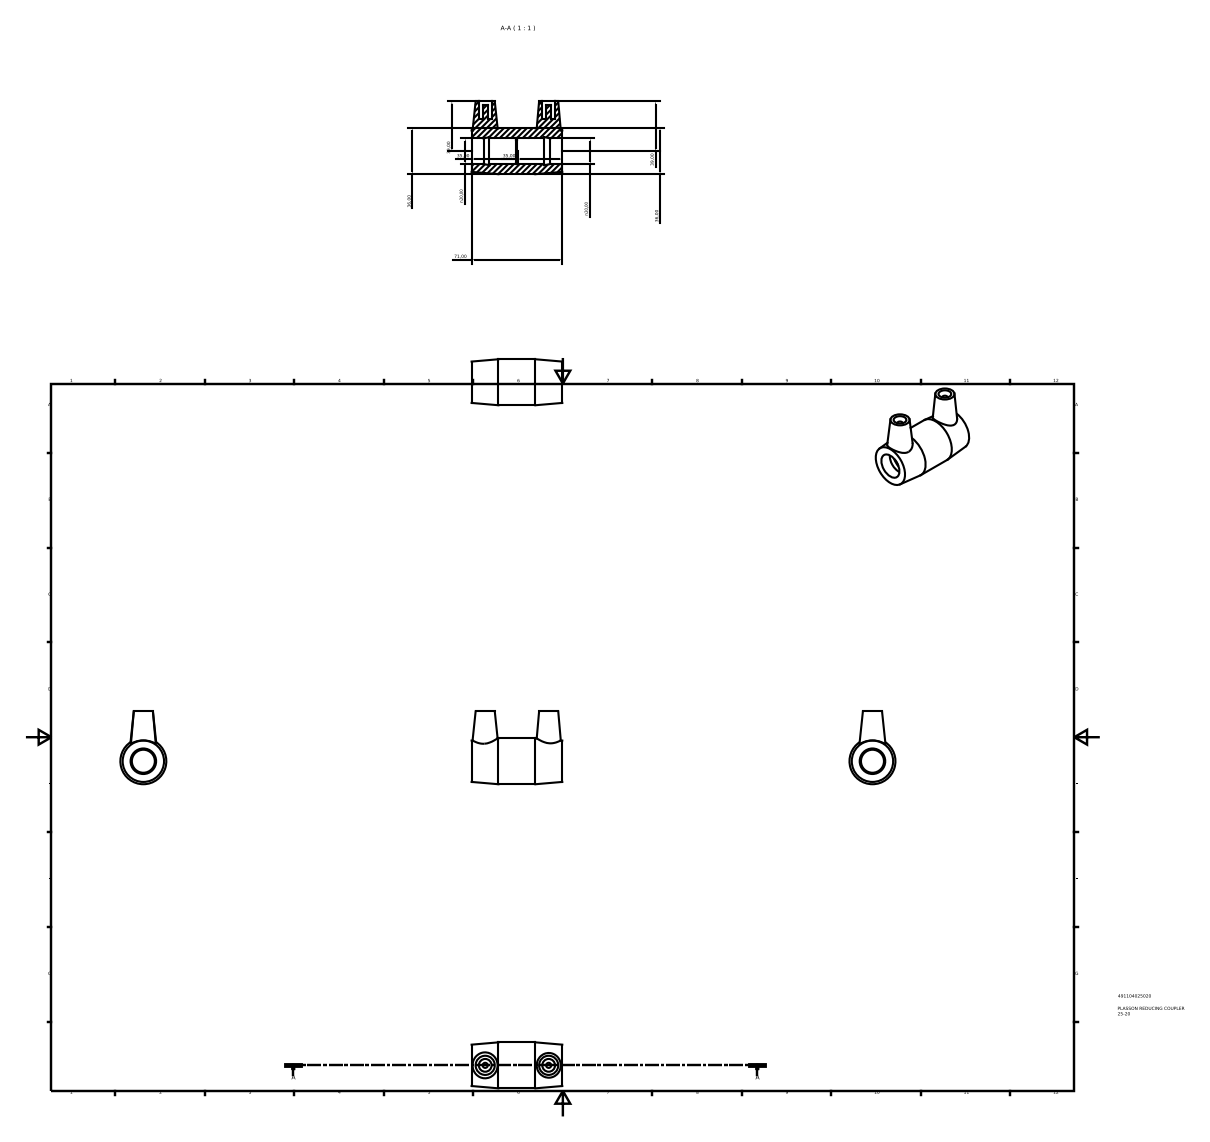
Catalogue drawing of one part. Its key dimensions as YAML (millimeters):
part_name: "491104025020"
step_written_by: "Autodesk Inventor 2015 (AUTOMOTIVE_DESIGN)"
units: millimeters
bodies: {solids: 1, faces: 28, planar: 12, cylindrical: 10, other: 6}
overall_size: [71, 57, 36]
volume: 54209
surface_area: 17009
round_holes:
  - {diameter: 10, count: 2}
  - {diameter: 18, count: 1}
  - {diameter: 20, count: 1}
round_bosses_or_shafts:
  - {diameter: 4, count: 2}
  - {diameter: 36, count: 1}
face_to_face_distances: [71, 14, 57, 43, 35.91, 21.91, 21.09, 35.09, 35, 21]
hole_center_spacings: [49.7]
